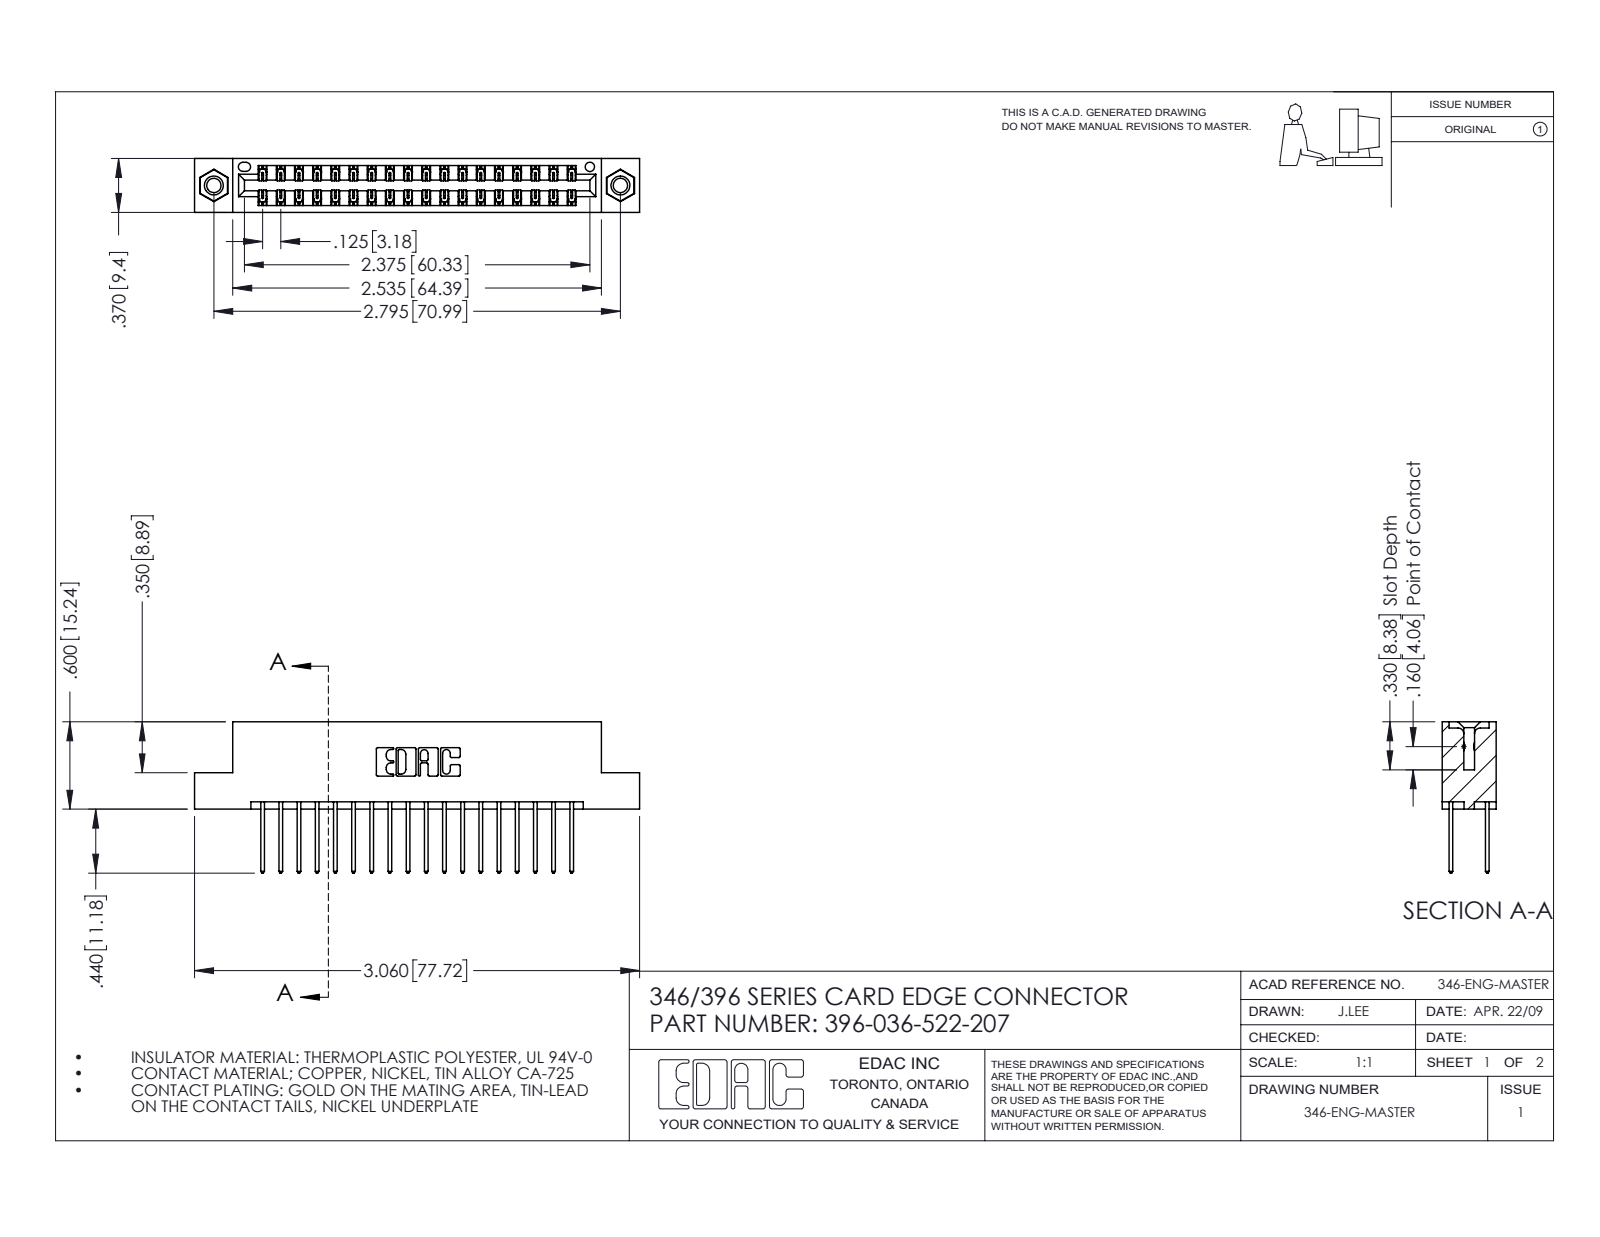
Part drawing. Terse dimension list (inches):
name: 346 Part_Flush Mounting Lugs - 0.156 Dia-TI; 345-292-001_345-293-122; 345-250-001_345-250-005-103; 396-036-522-207
written by: SolidWorks 2016 (CONFIG_CONTROL_DESIGN)
unit: in
bodies: 39 solids, 2054 faces (1368 planar, 670 cylindrical, 16 other)
size: 3.06 × 1.04 × 0.37
volume: 0.456 in³; area: 16.05 in²
holes: 2× ⌀0.098, 2× ⌀0.125, 2× ⌀0.156, 1× ⌀0.064
bosses: 2× ⌀0.155
rounds: 54× R0.006, 36× R0.01, 22× R0.01, 6× R0.007, 6× R0.031, 3× R0.026, 2× R0.014, 2× R0.022
face distances: 0.048, 0.322, 0.25, 0.37, 0.072, 0.298, 0.025, 0.275, 0.148, 0.222
hole spacings: 0.246, 2.588, 2.795
